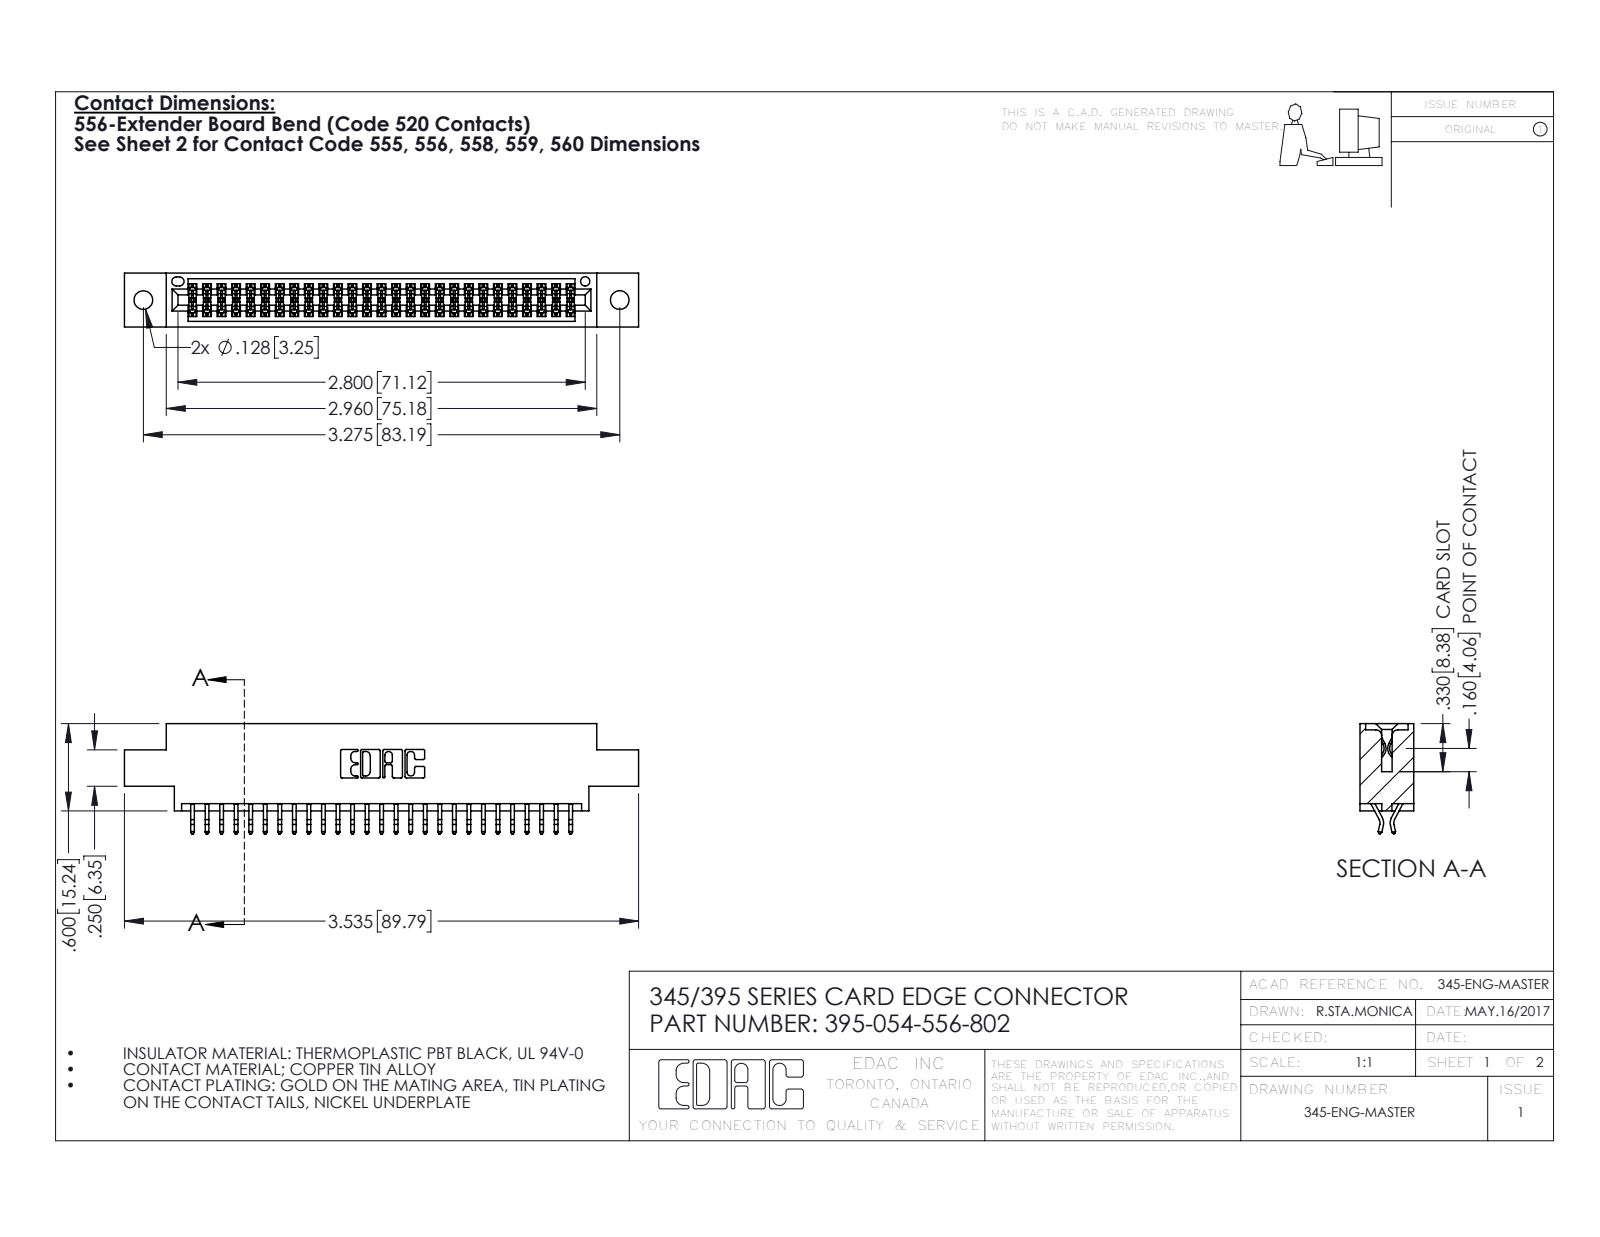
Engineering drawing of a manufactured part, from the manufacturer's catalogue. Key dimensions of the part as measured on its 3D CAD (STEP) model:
Part name (STEP PRODUCT): 345 Part_0.170 Offset - 0.128 Dia; 345-292-001_556 Tail; 395-054-556-802
STEP written by: SolidWorks 2016 (CONFIG_CONTROL_DESIGN)
Units: inches
Bodies: 55 solids, 3154 faces (2082 planar, 1072 cylindrical, 0 other)
Overall size (bounding box): 3.535 × 0.757 × 0.37
Volume: 0.514 in³ · Surface area: 18.59 in²
Round holes (diameter × count): ⌀0.128 ×2, ⌀0.064 ×1
Partial cylindrical surfaces — rounded edges, fillets, slot ends (radius × count): R0.006 ×81, R0.01 ×22, R0.007 ×6, R0.031 ×6, R0.026 ×3, R0.01 ×2, R0.014 ×2, R0.019 ×2
Main face-to-face distances: 0.298, 0.072, 0.37, 0.2, 0.025, 0.098, 0.272, 0.225, 0.175, 0.149
Hole centre spacings: 0.27, 3.04, 3.275
